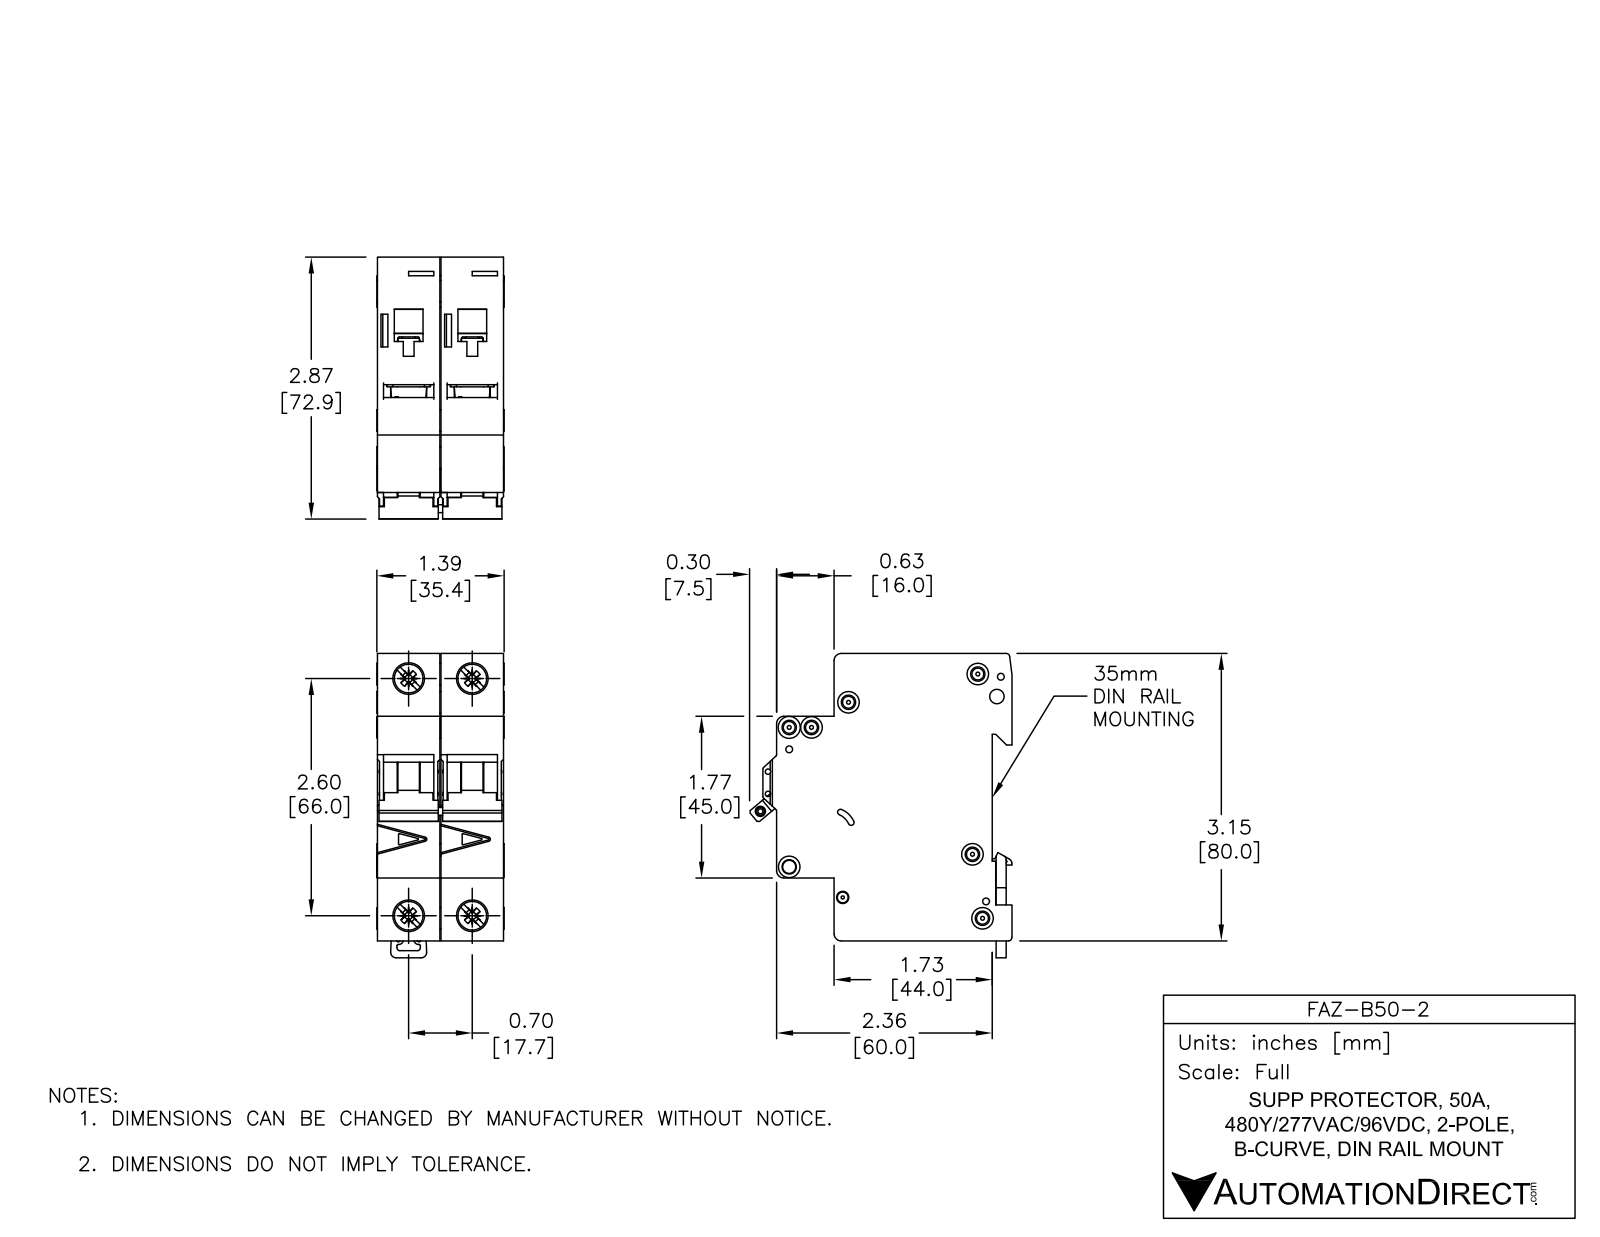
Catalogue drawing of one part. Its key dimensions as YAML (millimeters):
part_name: "FAZ-B50-2"
step_written_by: "SolidWorks 2014 (AUTOMOTIVE_DESIGN)"
units: millimeters
bodies: {solids: 8, faces: 1104, planar: 466, cylindrical: 396, other: 242}
overall_size: [84.78, 73.04, 35.4]
volume: 149808
surface_area: 38799
round_holes:
  - {diameter: 3.6, count: 6}
  - {diameter: 1.9, count: 3}
  - {diameter: 1.09, count: 2}
  - {diameter: 1.5, count: 2}
  - {diameter: 4, count: 2}
  - {diameter: 7.15, count: 2}
  - {diameter: 8.2, count: 2}
  - {diameter: 2.15, count: 1}
  - {diameter: 2.2, count: 1}
  - {diameter: 2.55, count: 1}
  - {diameter: 3.3, count: 1}
  - {diameter: 3.4, count: 1}
round_bosses_or_shafts:
  - {diameter: 6, count: 4}
  - {diameter: 8.2, count: 2}
  - {diameter: 2.5, count: 2}
partial_cylinders:
  - {radius: 0.25, count: 49}
  - {radius: 0.5, count: 19}
  - {radius: 2, count: 10}
  - {radius: 0.2, count: 8}
  - {radius: 1, count: 8}
  - {radius: 0.8, count: 2}
  - {radius: 1.8, count: 2}
  - {radius: 3, count: 2}
face_to_face_distances: [17.7, 17.5, 35.2, 79.48, 5.5, 49.5, 44, 65.5, 60, 16]
hole_center_spacings: [6.2, 13.64, 17.7, 66, 68.33, 4.81, 5.19, 5.61]
